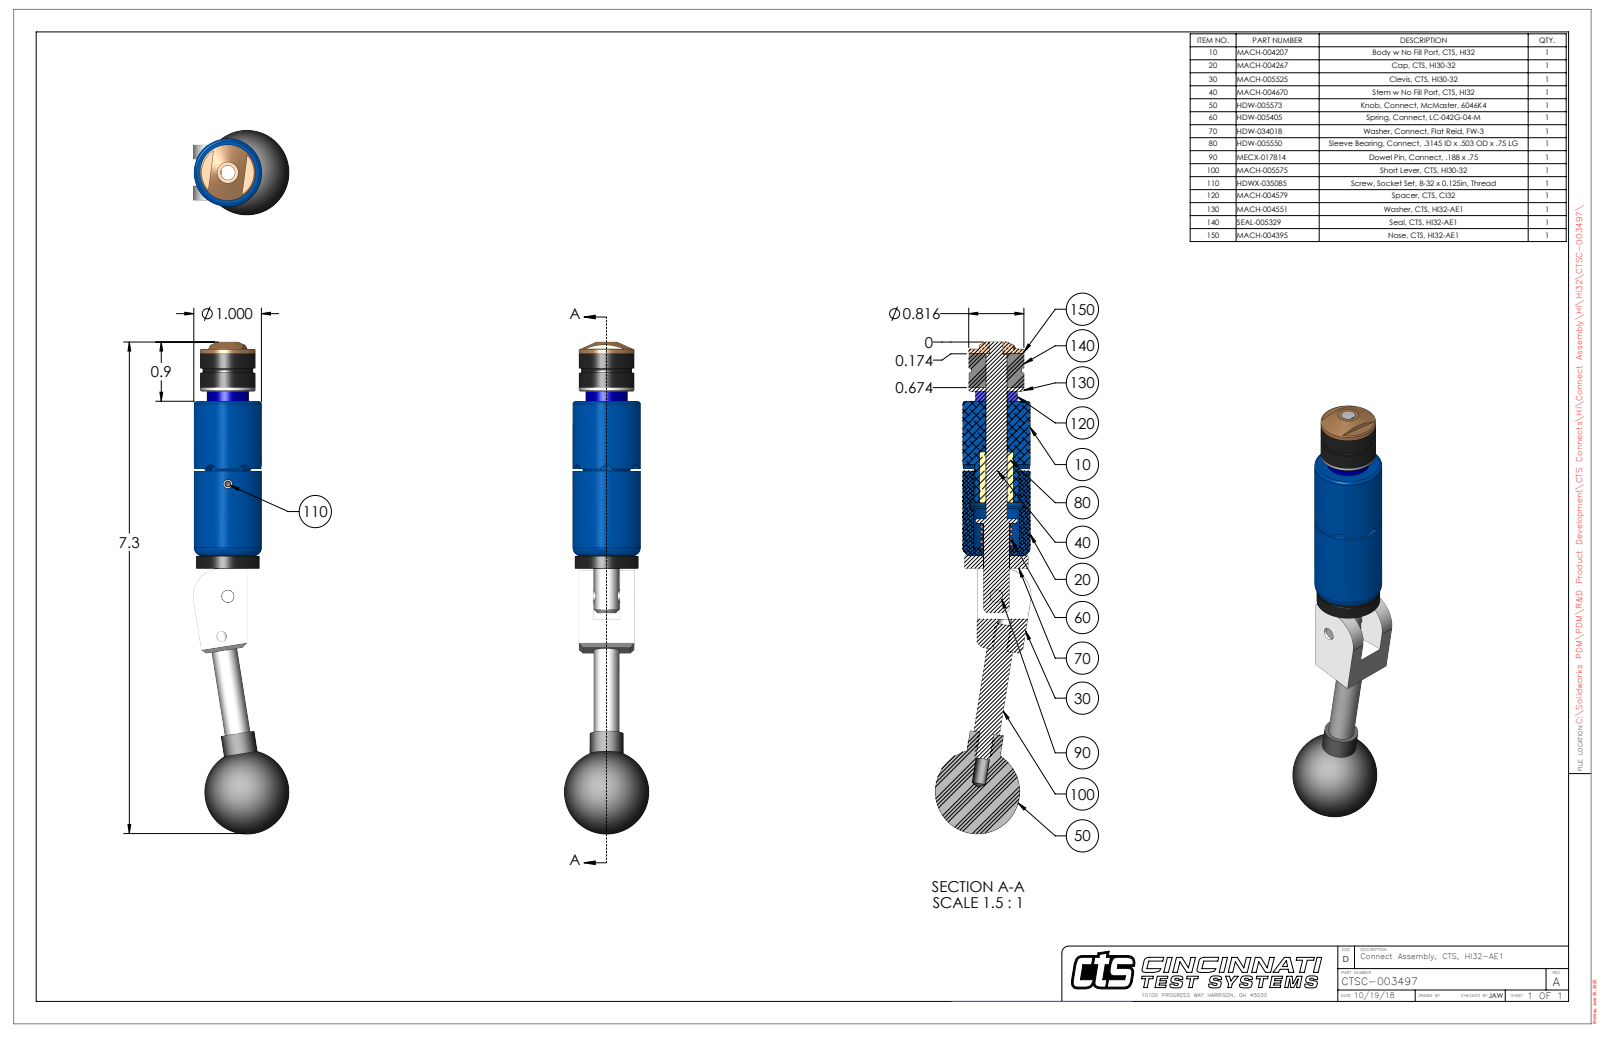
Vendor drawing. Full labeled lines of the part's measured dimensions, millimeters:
Part name (STEP PRODUCT): CTSC-003497
STEP written by: SolidWorks 2023 (AUTOMOTIVE_DESIGN)
Units: millimetres
Bodies: 10 solids, 254 faces (97 planar, 100 cylindrical, 57 other)
Overall size (bounding box): 184.6 × 36 × 31.8
Volume: 66 200 mm³ · Surface area: 22 540 mm²
Round holes (diameter × count): ⌀5.1 ×2, ⌀3.5 ×1, ⌀3.8 ×1, ⌀4.8 ×1, ⌀5.4 ×1, ⌀7.9 ×1, ⌀8 ×1, ⌀8 ×1, ⌀9.8 ×1, ⌀10 ×1
Round bosses / shafts (diameter × count): ⌀6.4 ×2, ⌀5.1 ×2, ⌀25.4 ×1, ⌀23.8 ×1, ⌀20.7 ×1, ⌀15.7 ×1, ⌀12.7 ×1, ⌀9.7 ×1
Partial cylindrical surfaces — rounded edges, fillets, slot ends (radius × count): R2.4 ×6, R0.7 ×2, R8.7 ×1, R10.2 ×1, R11.9 ×1
Main face-to-face distances: 5.3, 15.3, 12.7, 75.8, 63.1, 17.8, 5.1, 58, 20.6, 80.6
Hole centre spacings: 15.2, 42.1, 57.2
